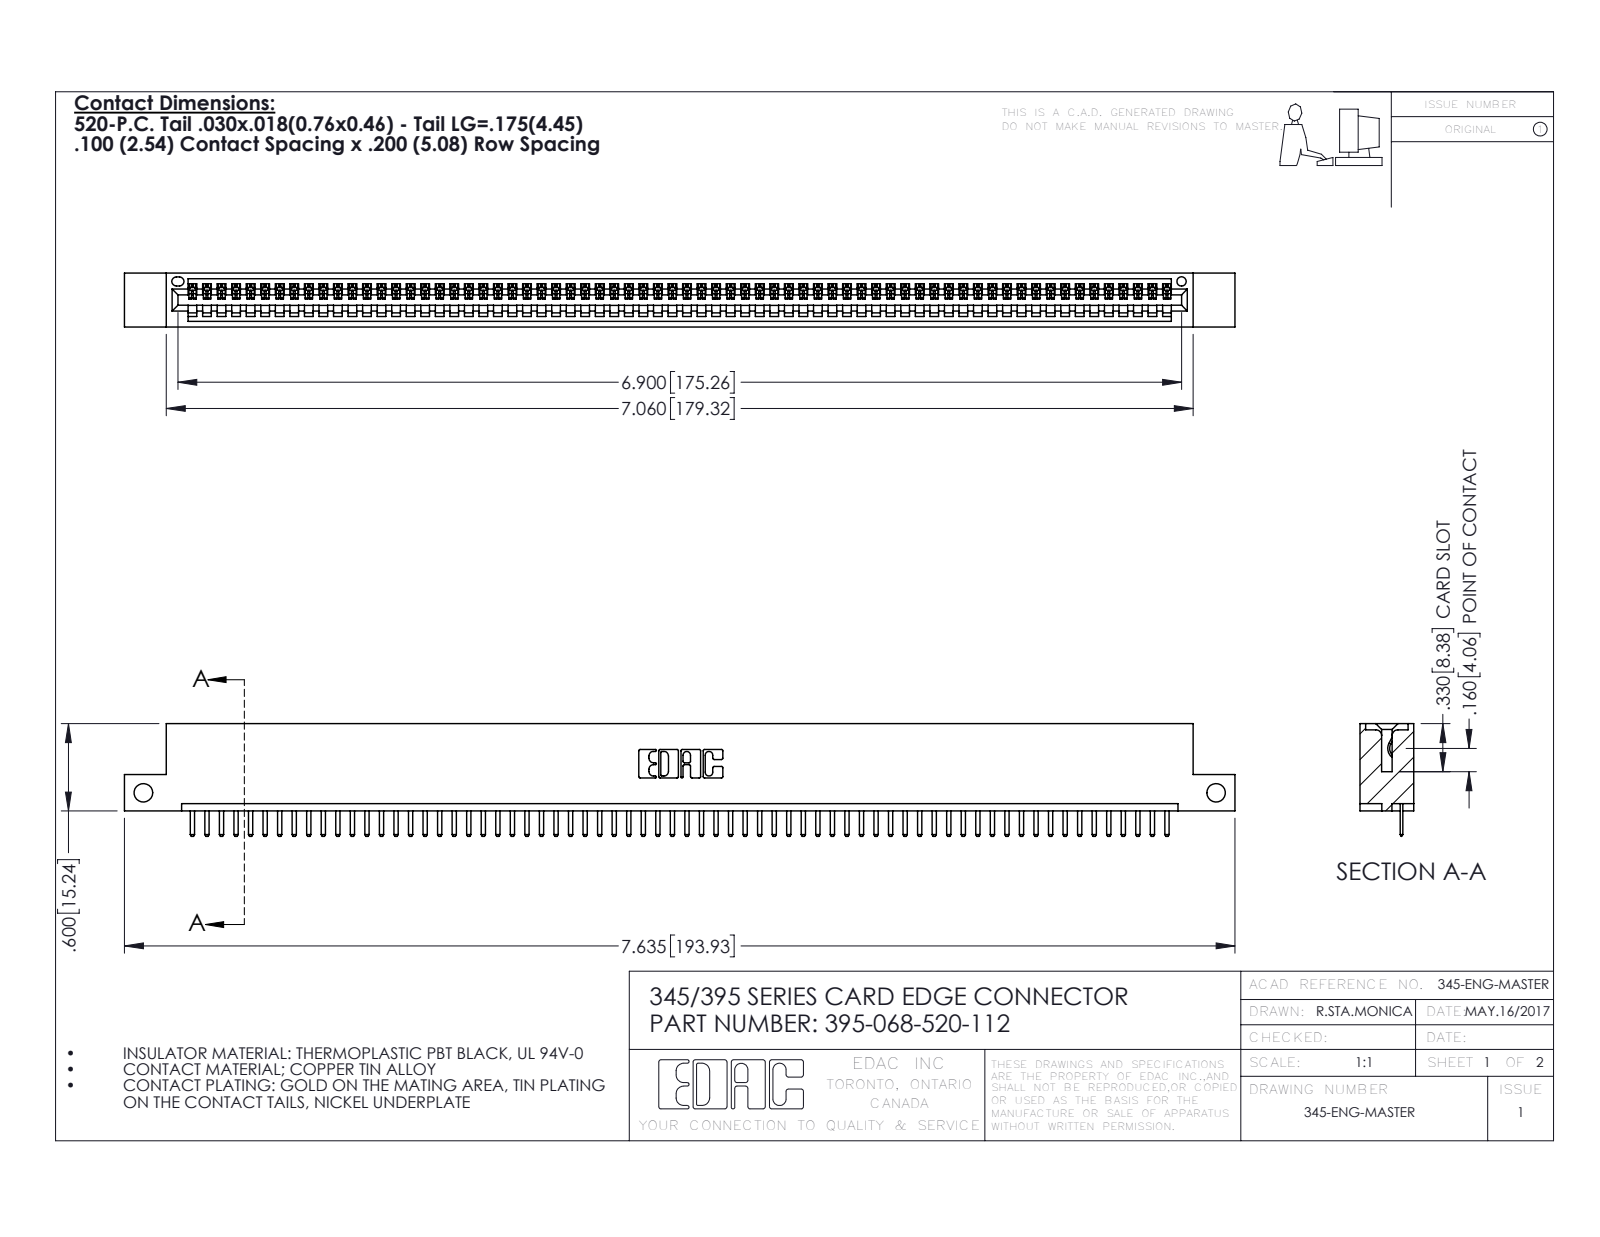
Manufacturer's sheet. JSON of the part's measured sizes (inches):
{"part_name": "395-068-520-112; 345-292-001_345-293-120; 345 Part_Flush Mounting Lugs - Side Mount", "step_written_by": "SolidWorks 2016 (CONFIG_CONTROL_DESIGN)", "units": "inches", "bodies": {"solids": 69, "faces": 4342, "planar": 2936, "cylindrical": 1406, "other": 0}, "overall_size": [7.635, 0.775, 0.37], "volume_in3": 1.12, "surface_area_in2": 37.13, "round_holes": [[0.128, 2], [0.064, 1]], "partial_cylinders_radius": [[0.01, 138], [0.006, 136], [0.01, 22], [0.007, 6], [0.031, 6], [0.026, 3], [0.031, 2], [0.04, 2]], "face_to_face_distances": [0.298, 0.072, 0.37, 0.2, 0.098, 0.272, 0.025, 0.225, 0.072, 0.149], "hole_center_spacings": [7.375]}
